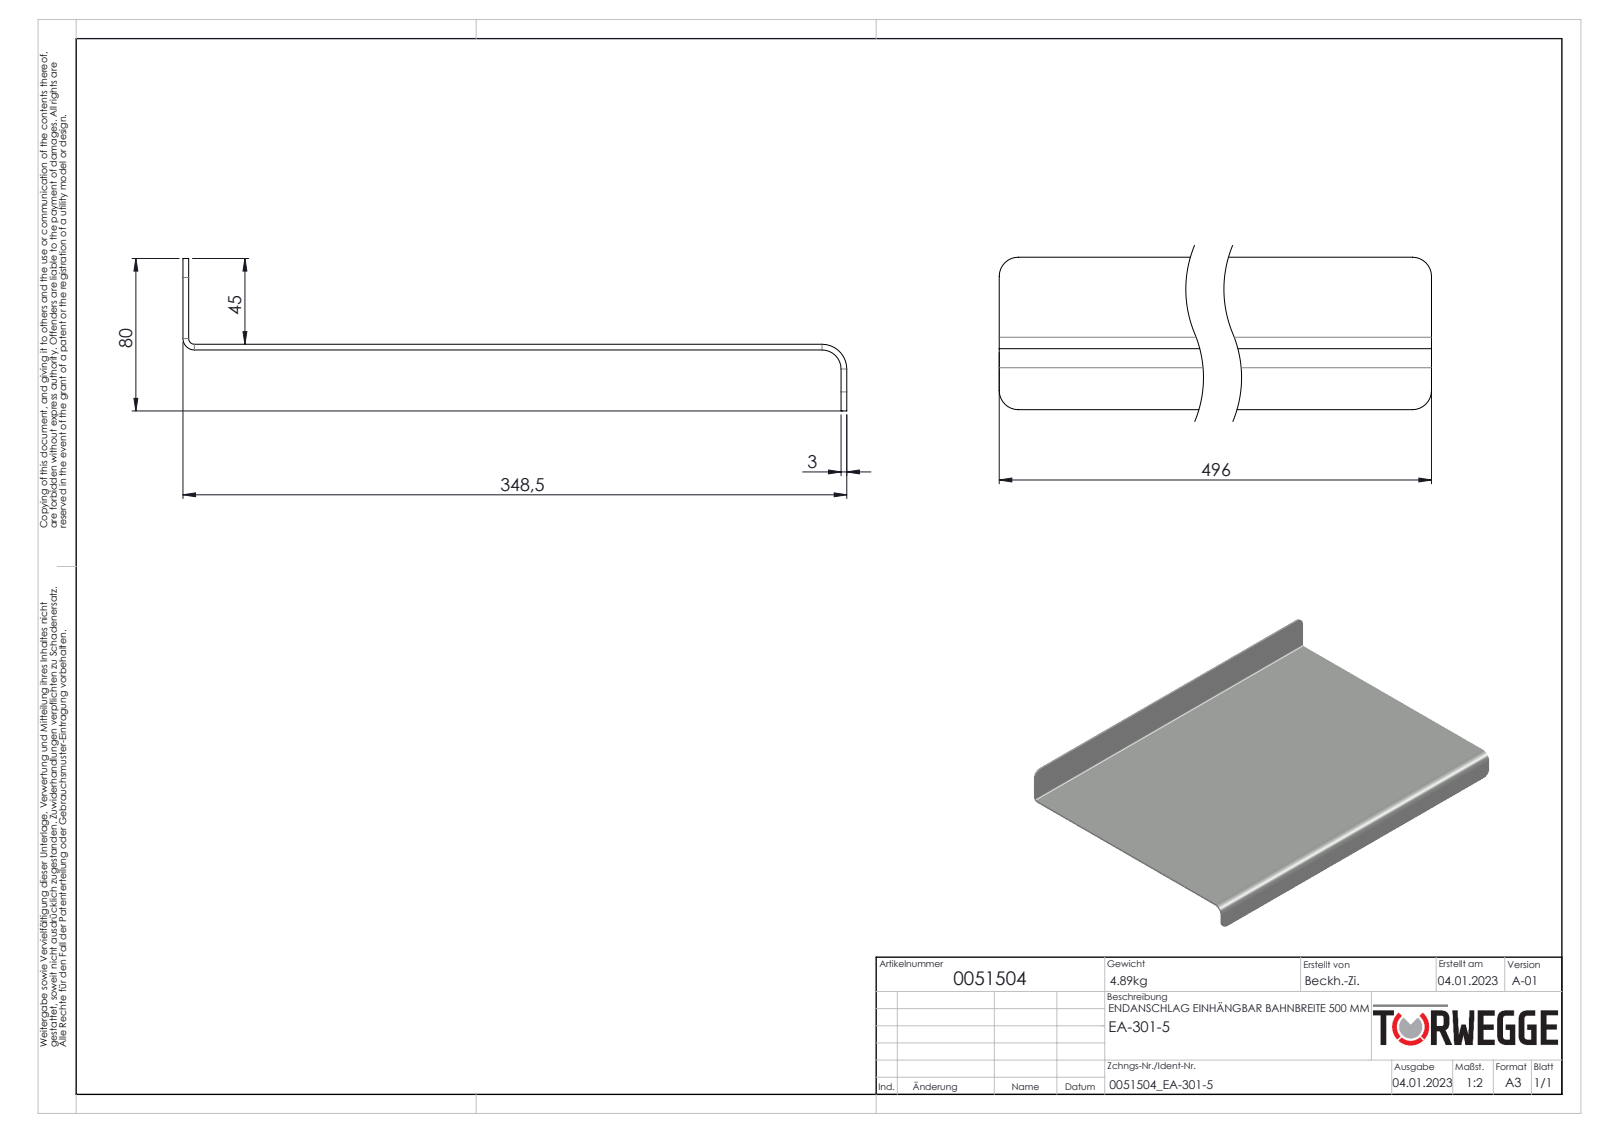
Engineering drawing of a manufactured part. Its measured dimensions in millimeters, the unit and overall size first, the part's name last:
Units: millimetres
Overall size (bounding box): 496 × 348.5 × 80
Partial cylindrical surfaces — rounded edges, fillets, slot ends (radius × count): R10 ×5, R3 ×1, R6 ×1, R13 ×1
Main face-to-face distances: 3, 345.5, 342.5, 348.5, 32, 35, 80, 48, 45, 496
Volume: 622 668 mm³ · Surface area: 420 548 mm²
Bodies: 1 solid, 26 faces (18 planar, 8 cylindrical, 0 other)
Part name (STEP PRODUCT): 0051504
STEP written by: SolidWorks 2020 (AUTOMOTIVE_DESIGN)
